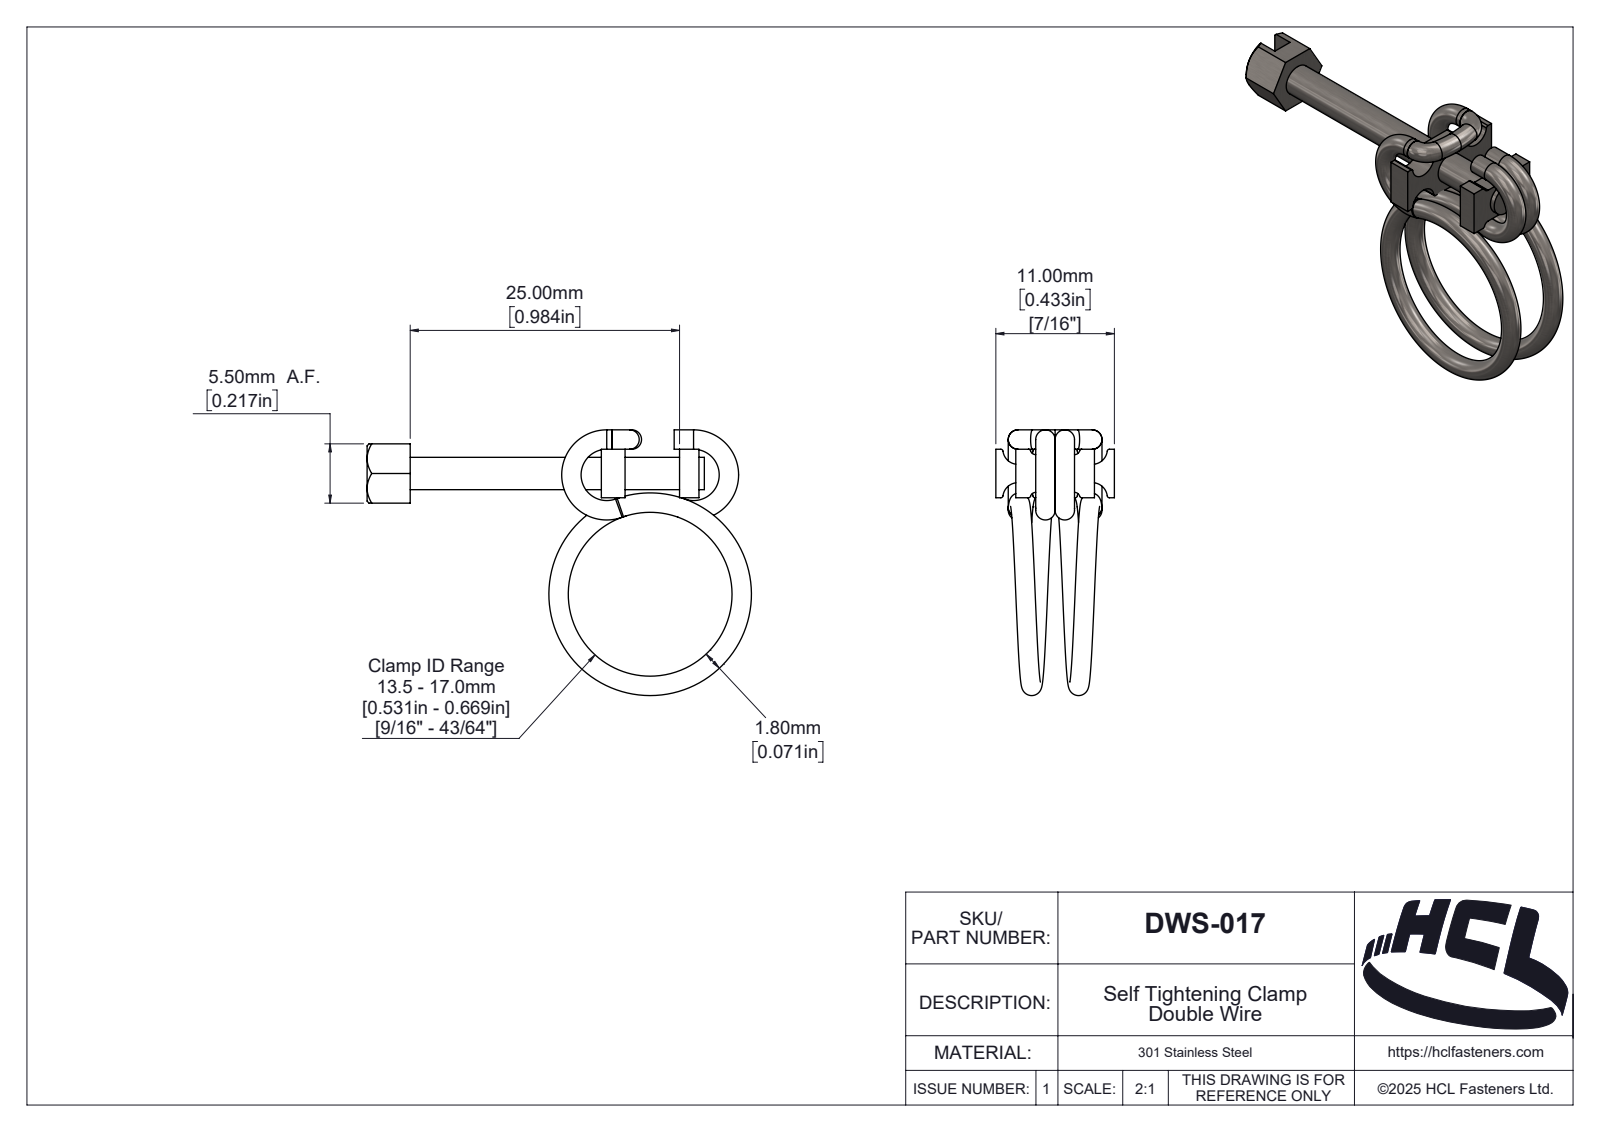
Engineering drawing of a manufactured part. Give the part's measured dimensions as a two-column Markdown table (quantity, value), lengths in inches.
| quantity | value |
| --- | --- |
| part name | DWS-017 |
| STEP written by | SolidWorks 2025 (AUTOMOTIVE_DESIGN) |
| units | inches |
| bodies | 6 solids, 209 faces (51 planar, 74 cylindrical, 84 other) |
| overall size | 1.404 × 0.97 × 0.433 |
| volume | 0.051 in³ |
| surface area | 2.613 in² |
| round holes (diameter × count) | 0.118 × 1 |
| round bosses / shafts (diameter × count) | 0.071 × 4 |
| partial cylindrical surfaces (radius × count) | 0.008 × 12, 0.02 × 4, 0.055 × 4, 0.016 × 1, 0.02 × 1, 0.021 × 1, 0.025 × 1, 0.036 × 1 |
| main face-to-face distances | 0.177, 0.02, 0.079, 0.217, 0.087, 0.157, 0.039, 0.286, 0.199, 0.357 |
